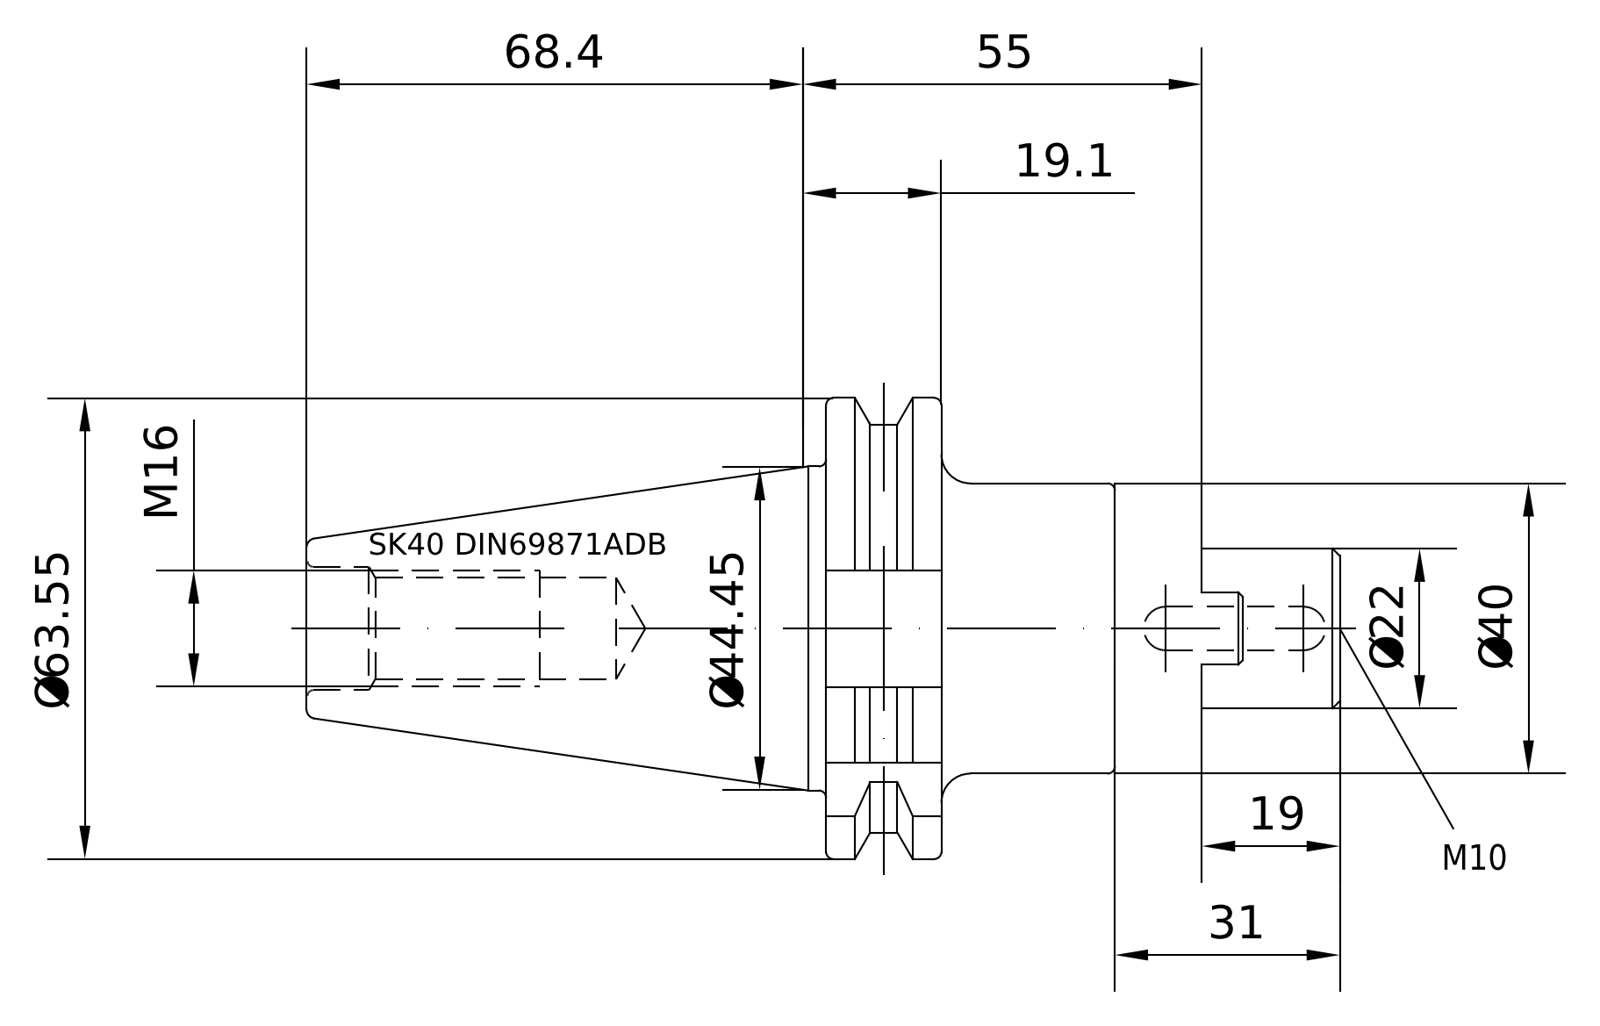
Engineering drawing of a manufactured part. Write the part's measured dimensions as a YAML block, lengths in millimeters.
part_name: "40-340-22; 85-200-22; 40-340-22_ASM"
step_written_by: "PRO/ENGINEER BY PARAMETRIC TECHNOLOGY CORPORATION, 2010430 (CONFIG_CONTROL_DESIGN)"
units: millimeters
bodies: {solids: 2, faces: 189, planar: 87, cylindrical: 44, other: 58}
overall_size: [142.25, 63.52, 61.42]
volume: 154674
surface_area: 32067
round_holes:
  - {diameter: 8.5, count: 1}
  - {diameter: 10, count: 1}
  - {diameter: 13.84, count: 1}
  - {diameter: 17.01, count: 1}
  - {diameter: 17.5, count: 1}
  - {diameter: 22.36, count: 1}
  - {diameter: 26, count: 1}
round_bosses_or_shafts:
  - {diameter: 43.75, count: 1}
  - {diameter: 40, count: 1}
  - {diameter: 22, count: 1}
  - {diameter: 16.01, count: 1}
partial_cylinders:
  - {radius: 1.35, count: 5}
  - {radius: 3, count: 2}
  - {radius: 5.05, count: 1}
  - {radius: 28, count: 1}
  - {radius: 31.76, count: 1}
face_to_face_distances: [39.8, 15.85, 23.95, 51.8, 35.95, 12, 1, 11, 70.8, 54.95]
